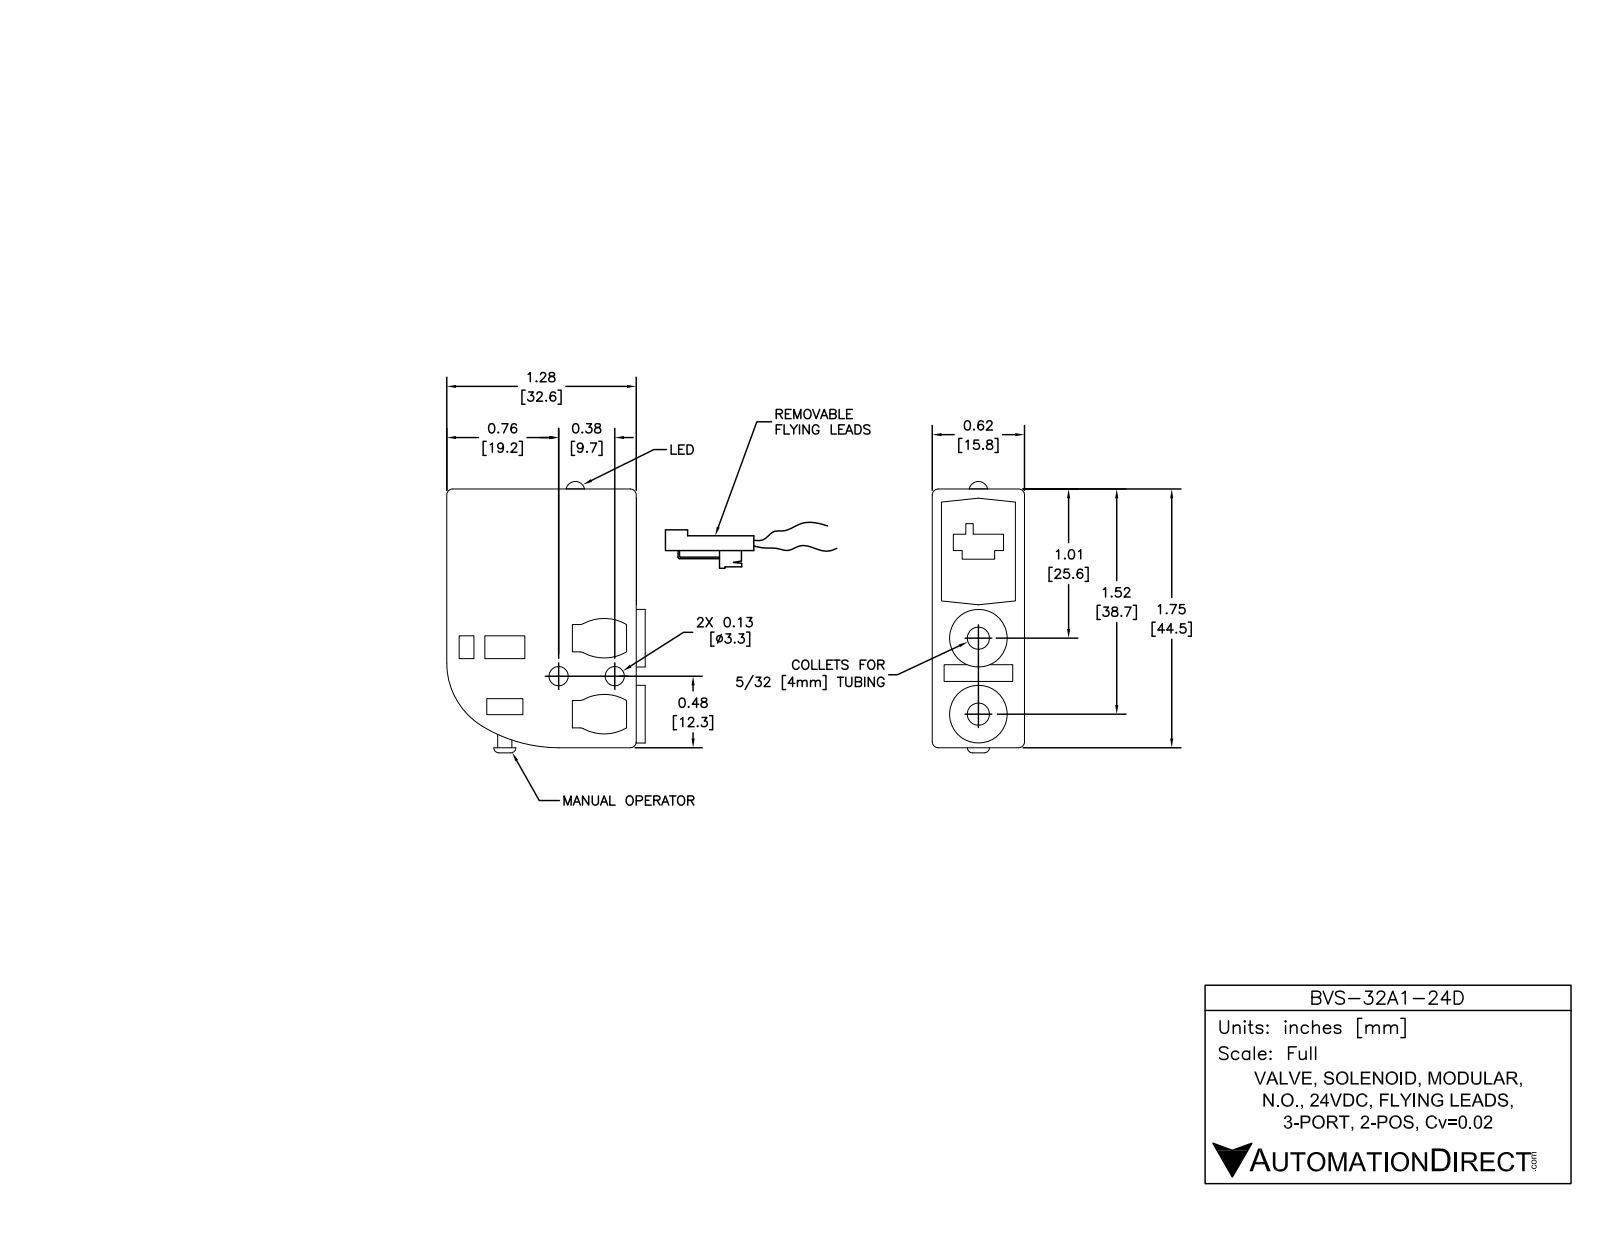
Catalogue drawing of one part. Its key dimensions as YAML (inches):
part_name: "BVS-32A1-24D"
step_written_by: "SolidWorks 2013 (AUTOMOTIVE_DESIGN)"
units: inches
bodies: {solids: 1, faces: 158, planar: 93, cylindrical: 52, other: 13}
overall_size: [1.836, 1.347, 0.624]
volume: 1.246
surface_area: 10.17
round_holes:
  - {diameter: 0.13, count: 2}
  - {diameter: 0.15, count: 2}
  - {diameter: 0.254, count: 2}
  - {diameter: 0.046, count: 1}
round_bosses_or_shafts:
  - {diameter: 0.39, count: 2}
  - {diameter: 0.124, count: 1}
  - {diameter: 0.096, count: 1}
partial_cylinders:
  - {radius: 0.04, count: 11}
  - {radius: 0.05, count: 4}
  - {radius: 0.3, count: 4}
  - {radius: 0.5, count: 1}
  - {radius: 1, count: 1}
face_to_face_distances: [0.624, 0.1, 0.524, 1.287, 1.288, 1.75, 0.424, 0.06, 0.059, 1.347]
hole_center_spacings: [0.061, 0.38, 0.453, 0.514]
